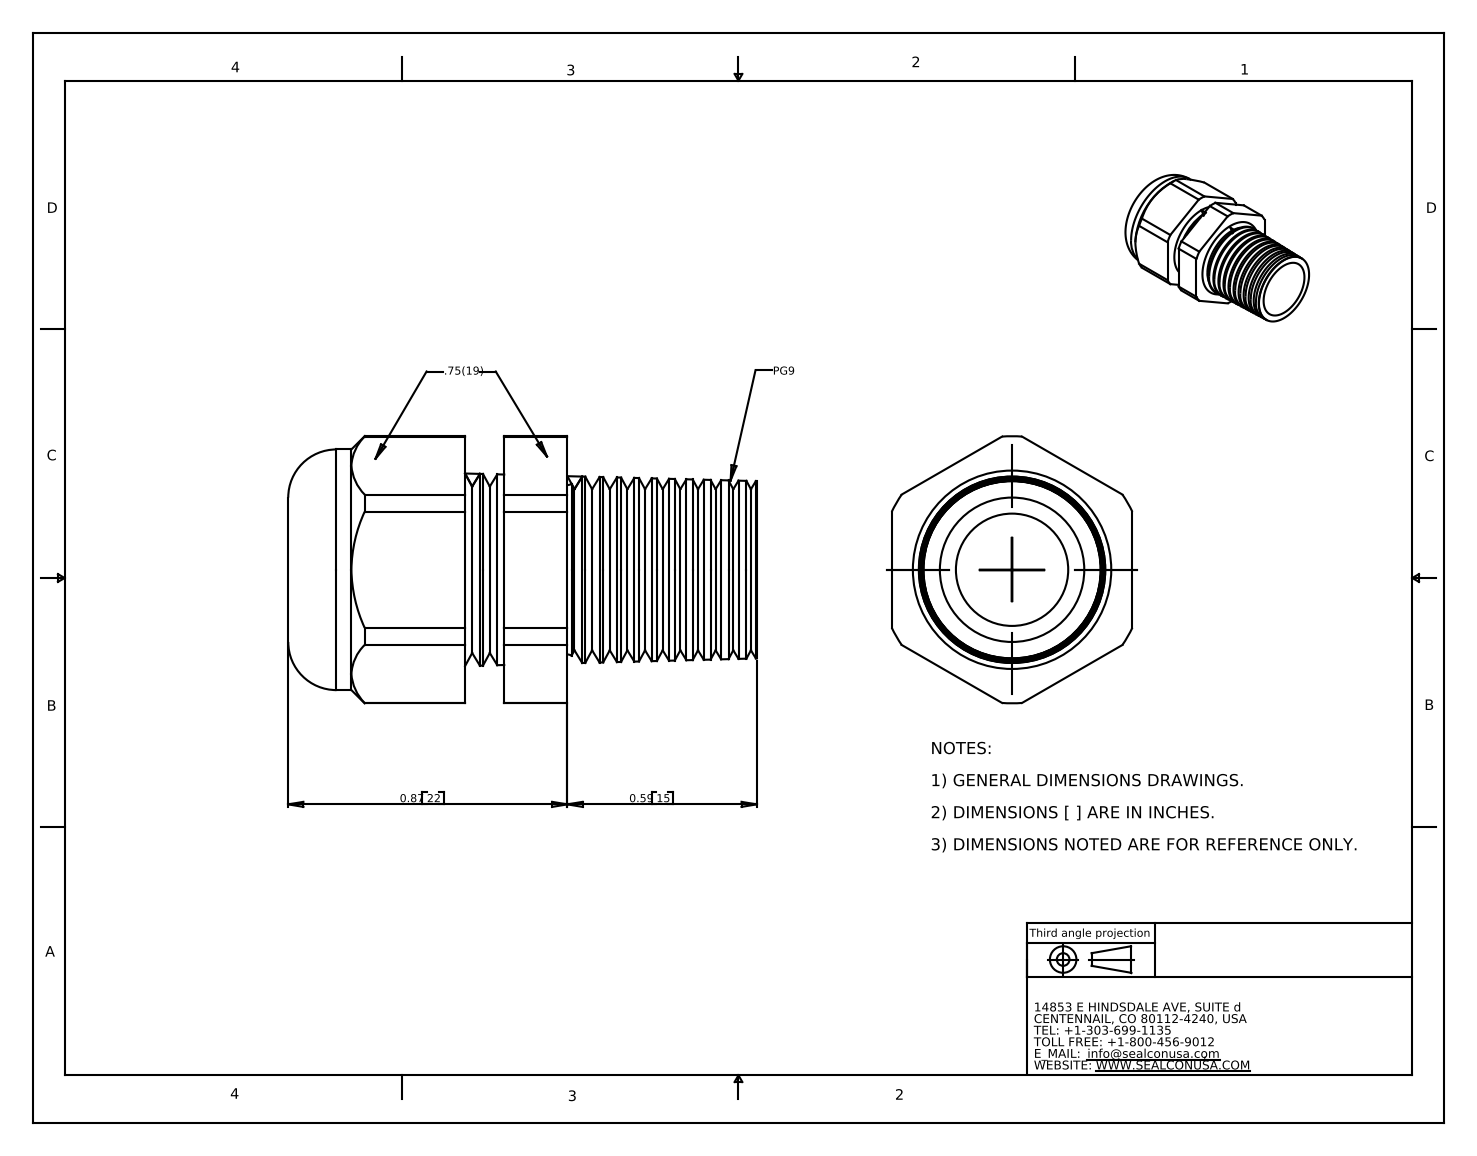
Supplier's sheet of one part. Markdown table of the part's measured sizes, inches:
| quantity | value |
| --- | --- |
| part name | CD09CA-GY |
| STEP written by | SolidWorks 2007 (CONFIG_CONTROL_DESIGN) |
| units | inches |
| bodies | 2 solids, 135 faces (19 planar, 22 cylindrical, 94 other) |
| overall size | 1.46 × 0.833 × 0.75 |
| volume | 0.34 in³ |
| surface area | 7.272 in² |
| round holes (diameter × count) | 0.35 × 1, 0.45 × 1 |
| round bosses / shafts (diameter × count) | 0.75 × 1 |
| partial cylindrical surfaces (radius × count) | 0.416 × 1 |
| main face-to-face distances | 0.75, 0.122, 0.75, 0.319, 0.197, 0.354, 0.476, 0.673, 1.263, 0.909 |
